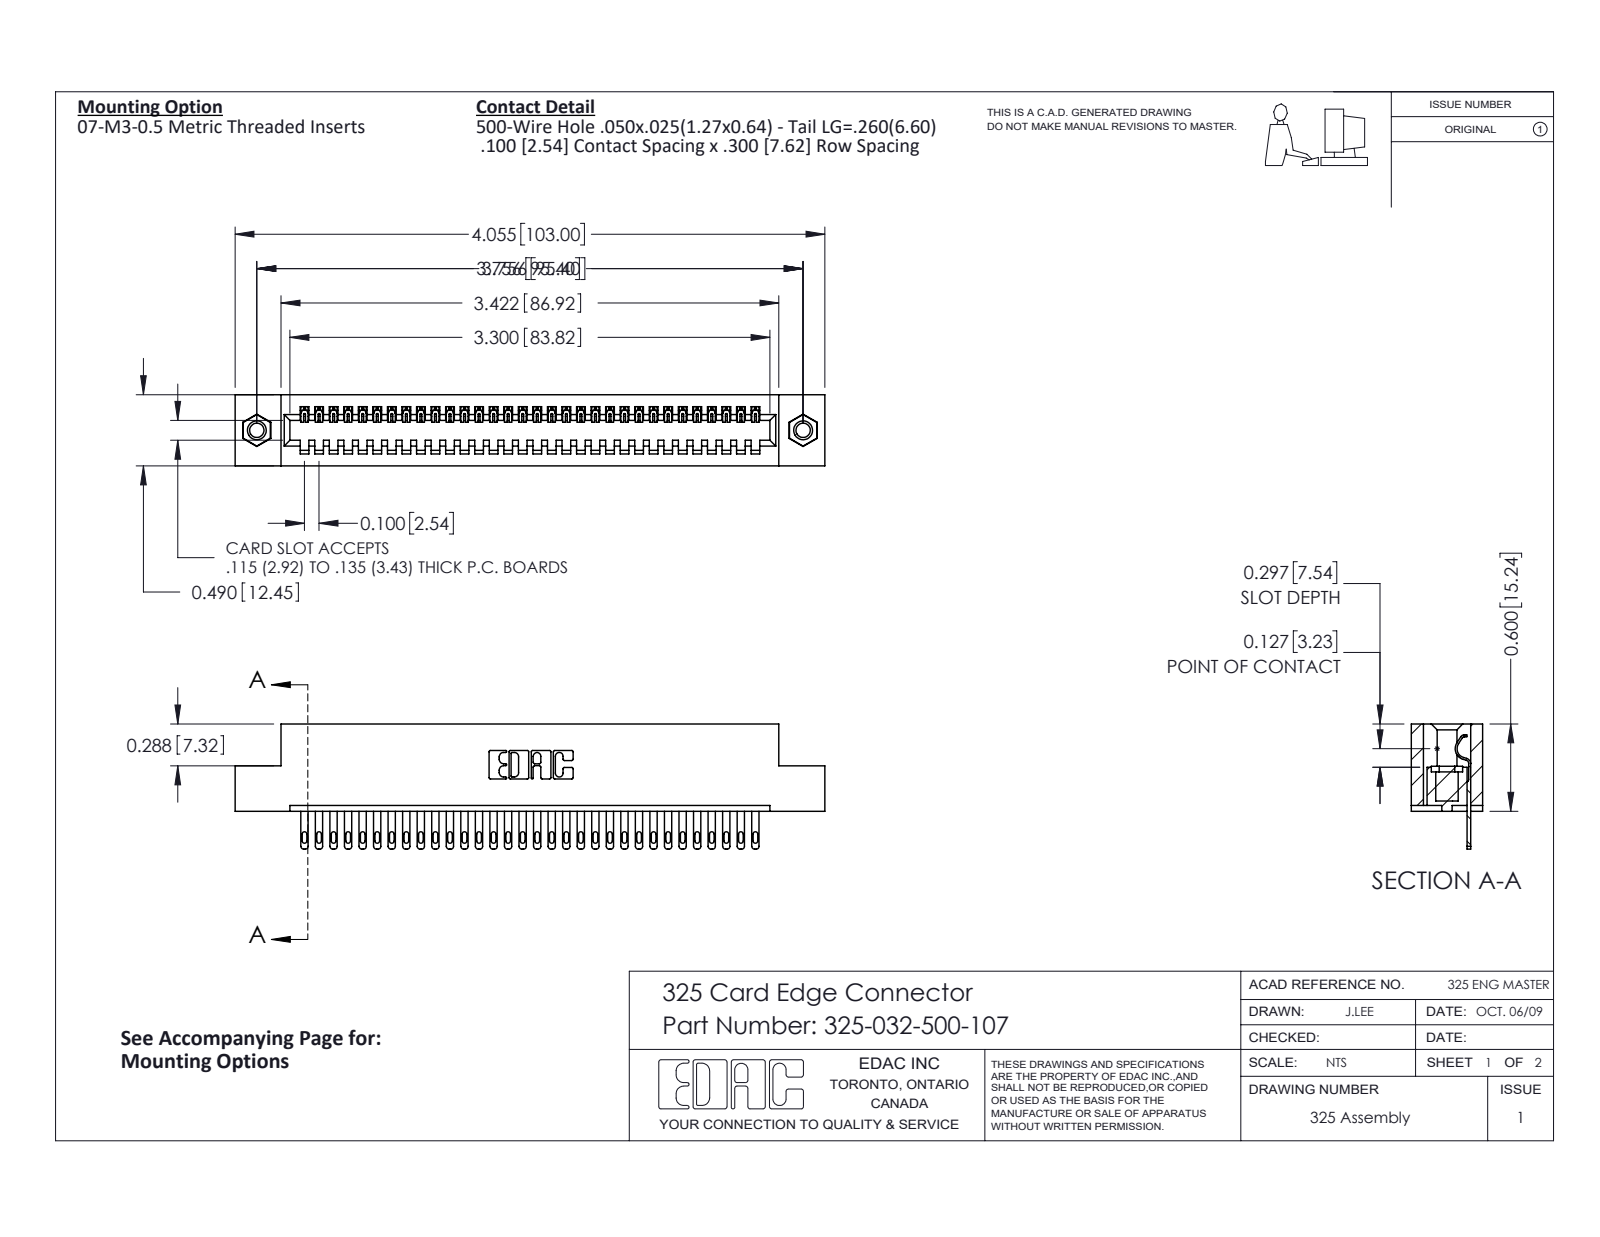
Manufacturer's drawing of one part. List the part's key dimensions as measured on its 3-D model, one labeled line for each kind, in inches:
Part name (STEP PRODUCT): 325-292-001_325-293-100; 325-032-500-107; 345-250-001_345-250-005-103; 325 Part_TI
STEP written by: SolidWorks 2016 (CONFIG_CONTROL_DESIGN)
Units: inches
Bodies: 35 solids, 1902 faces (1254 planar, 632 cylindrical, 16 other)
Overall size (bounding box): 4.055 × 0.86 × 0.49
Volume: 0.794 in³ · Surface area: 21.91 in²
Round holes (diameter × count): ⌀0.098 ×2, ⌀0.125 ×2, ⌀0.16 ×2
Round bosses / shafts (diameter × count): ⌀0.155 ×2
Partial cylindrical surfaces — rounded edges, fillets, slot ends (radius × count): R0.006 ×64, R0.016 ×64, R0.02 ×64, R0.01 ×22, R0.007 ×6, R0.031 ×6, R0.026 ×3, R0.014 ×1
Main face-to-face distances: 0.083, 0.407, 0.3, 0.49, 0.107, 0.383, 0.025, 0.325, 0.04, 0.1
Hole centre spacings: 3.756
